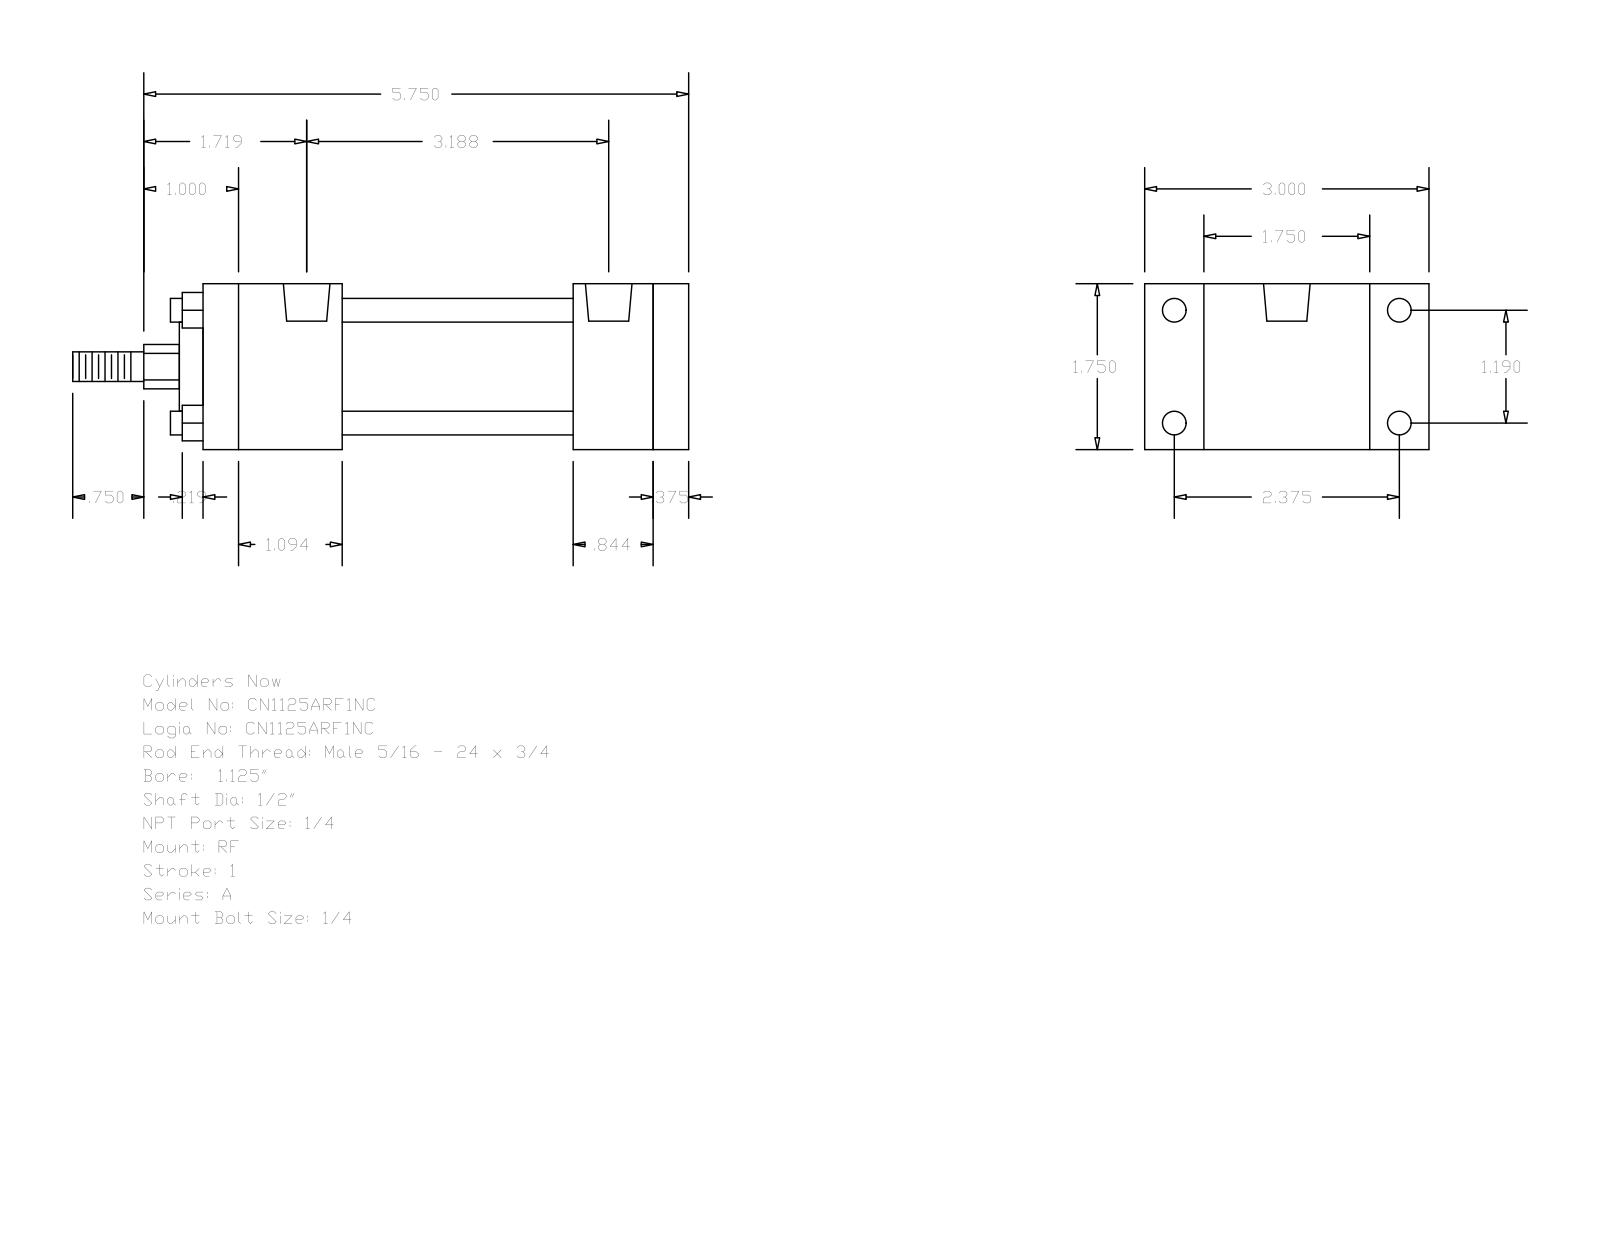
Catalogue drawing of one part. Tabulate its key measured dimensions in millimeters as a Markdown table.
| quantity | value |
| --- | --- |
| part name | A_RF__0112_0.5 |
| STEP written by | GSSL Pune (CONFIG_CONTROL_DESIGN) |
| units | millimeters |
| bodies | 0 solids, 92 faces (64 planar, 28 cylindrical, 0 other) |
| overall size | 165.1 × 76.2 × 44.45 |
| round holes (diameter × count) | 5.56 × 4, 6.35 × 4, 12.49 × 2 |
| round bosses / shafts (diameter × count) | 6.35 × 4, 31.88 × 1, 23.81 × 1, 12.7 × 1, 7.94 × 1 |
| partial cylindrical surfaces (radius × count) | 5.94 × 1 |
| main face-to-face distances | 44.46, 9.52, 120.65, 130.17, 37.3, 99.21, 61.91, 83.35, 92.87, 21.44 |
| hole center spacings | 30.22, 60.32, 67.47, 77.79, 1.58, 1.59, 79.37, 79.38 |
